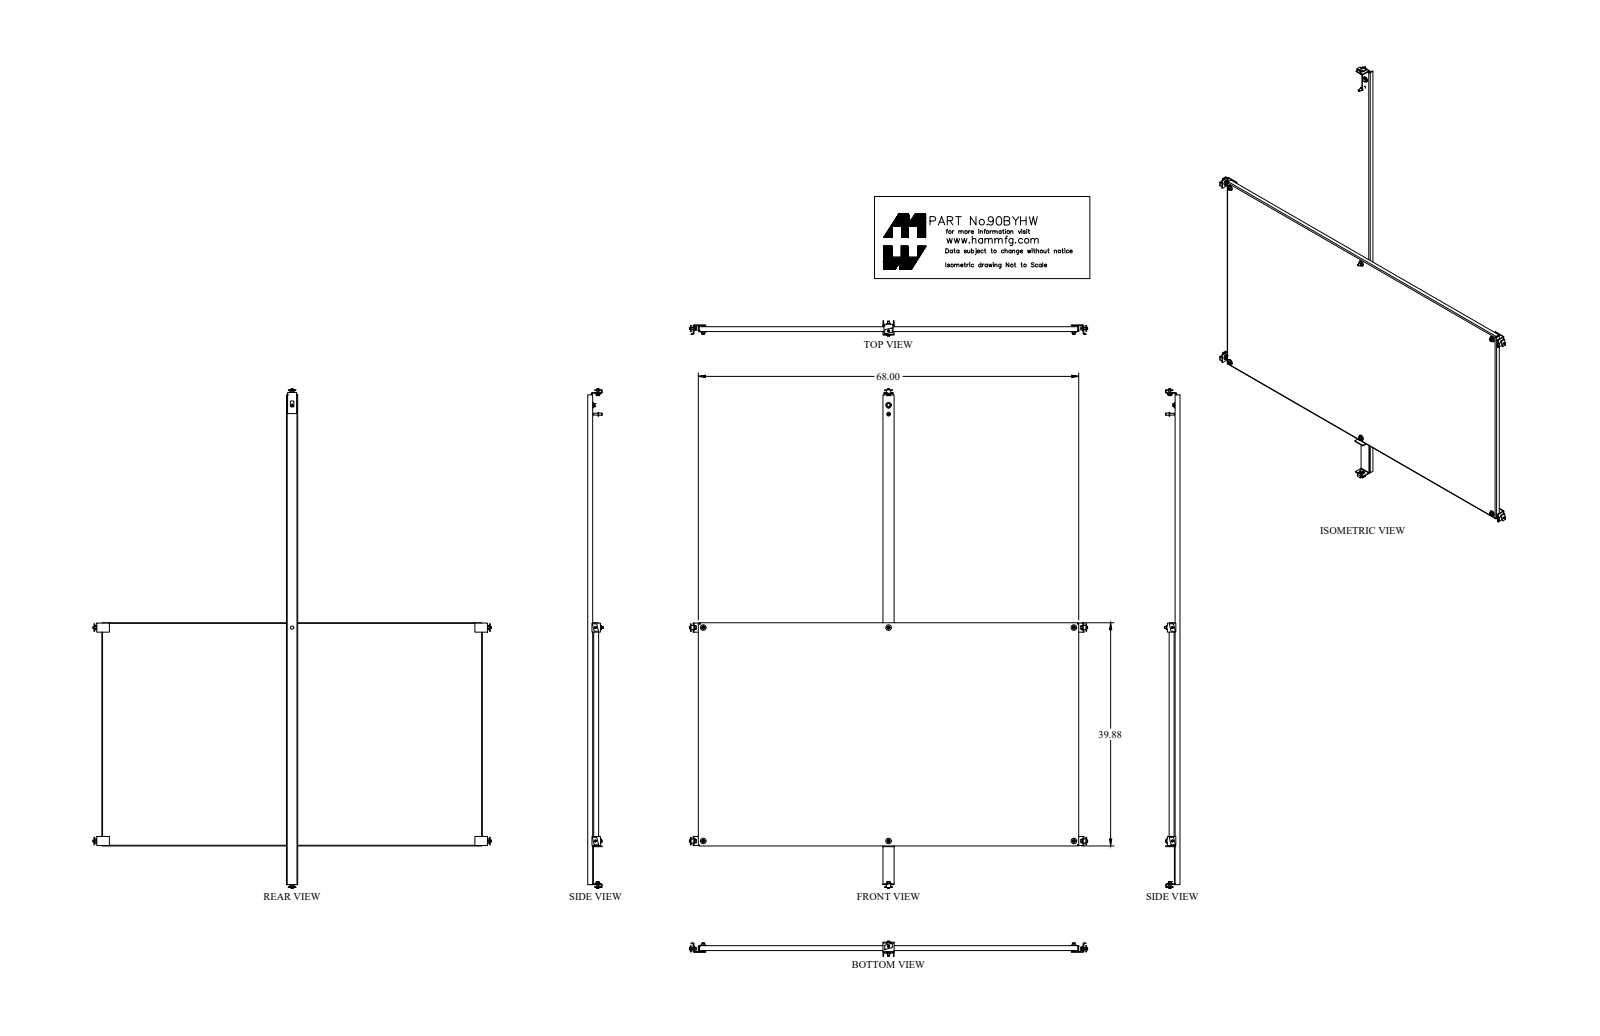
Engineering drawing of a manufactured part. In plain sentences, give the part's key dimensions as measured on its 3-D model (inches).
The part is named "90BYHW_Default". Its 3-D file was written by "SolidWorks 2018 (CONFIG_CONTROL_DESIGN)". It is 1 solid with 60 faces: 34 planar, 20 cylindrical and 6 other. Overall it measures 68 by 39.875 by 0.875 inches. Its volume is 357.5 cubic inches and its surface area 5 748 square inches. Round holes: 6 of diameter 0.563. Partial cylindrical surfaces (rounded edges, fillets, slot ends): 4 of radius 0.06, 4 of radius 0.185. The main face-to-face distances are 0.125, 39.75, 0.125, 67.875, 39.625, 39.875, 67.75, 68, 0.875, 0.75. The hole center spacings are 33.125, 50.506, 38.125, 66.25, 76.437.
